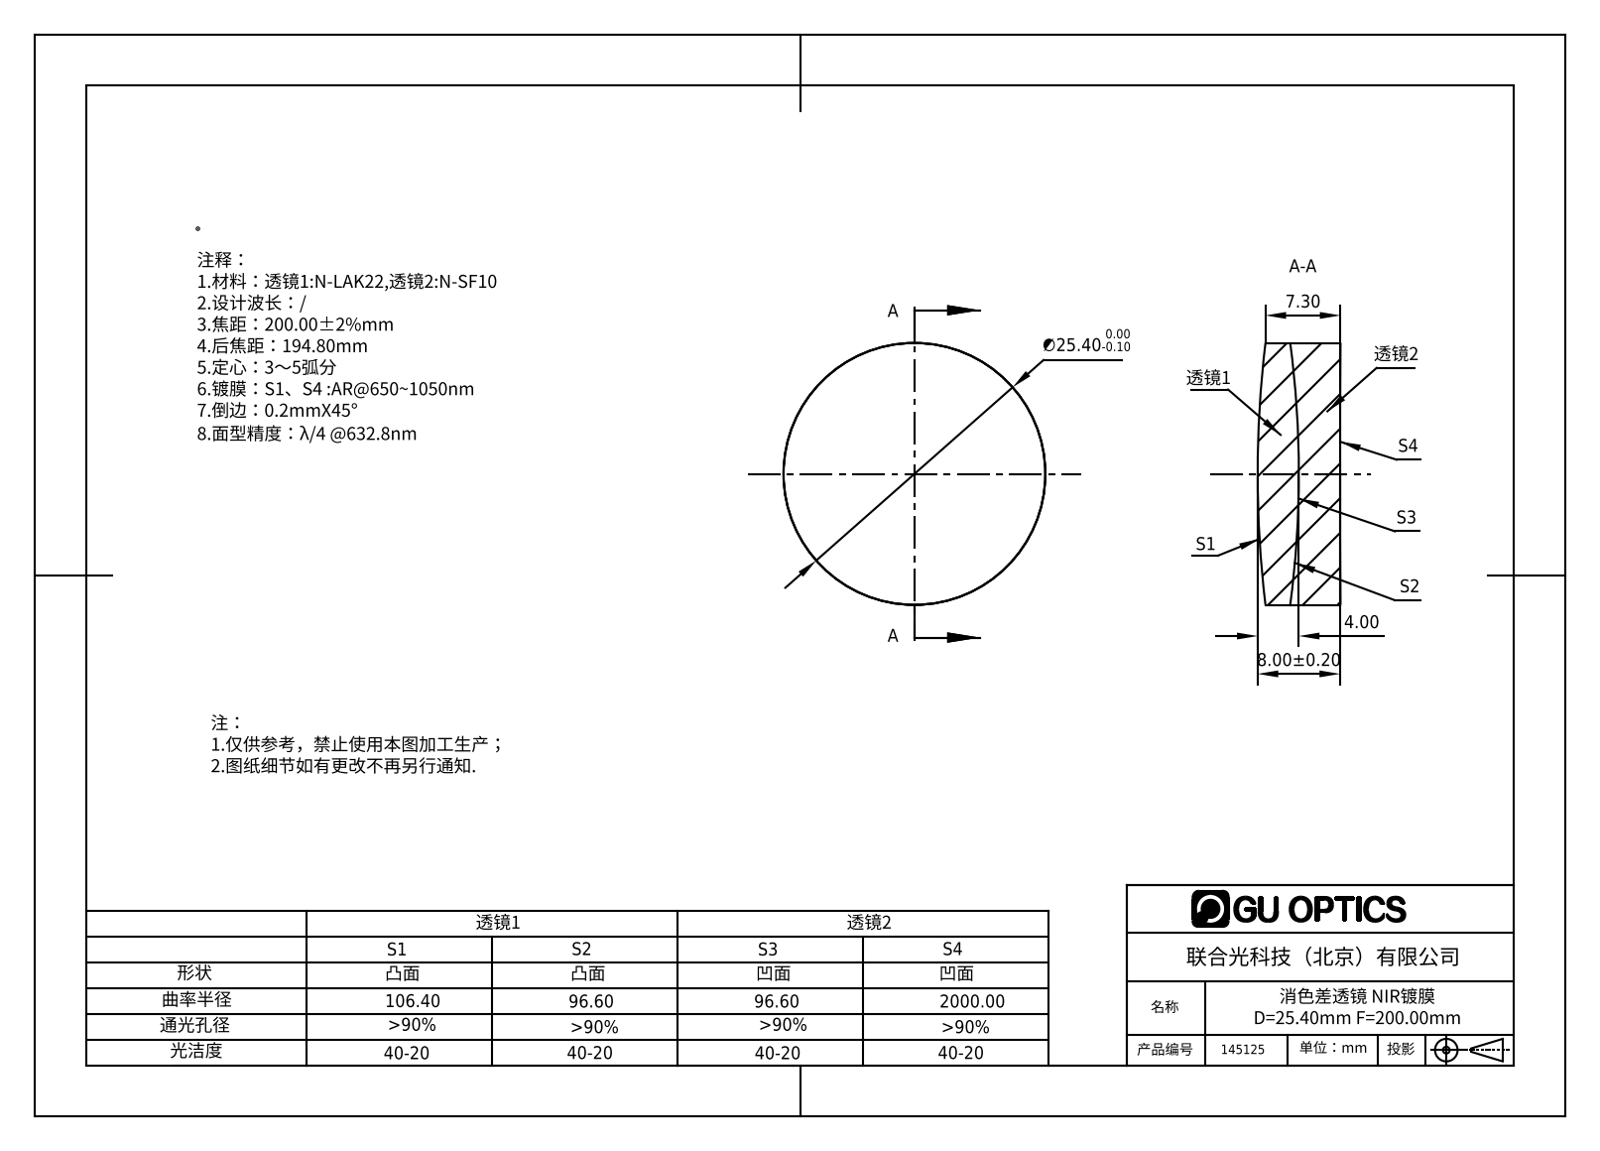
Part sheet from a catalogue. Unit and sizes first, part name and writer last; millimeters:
Units: millimetres
Overall size (bounding box): 25.4 × 25.4 × 8.04
Round bosses / shafts (diameter × count): ⌀25.4 ×1
Volume: 3 871 mm³ · Surface area: 2 614 mm²
Bodies: 2 solids, 12 faces (0 planar, 4 cylindrical, 8 other)
Part name (STEP PRODUCT): 145125
STEP written by: SolidWorks 2016 (AUTOMOTIVE_DESIGN)
